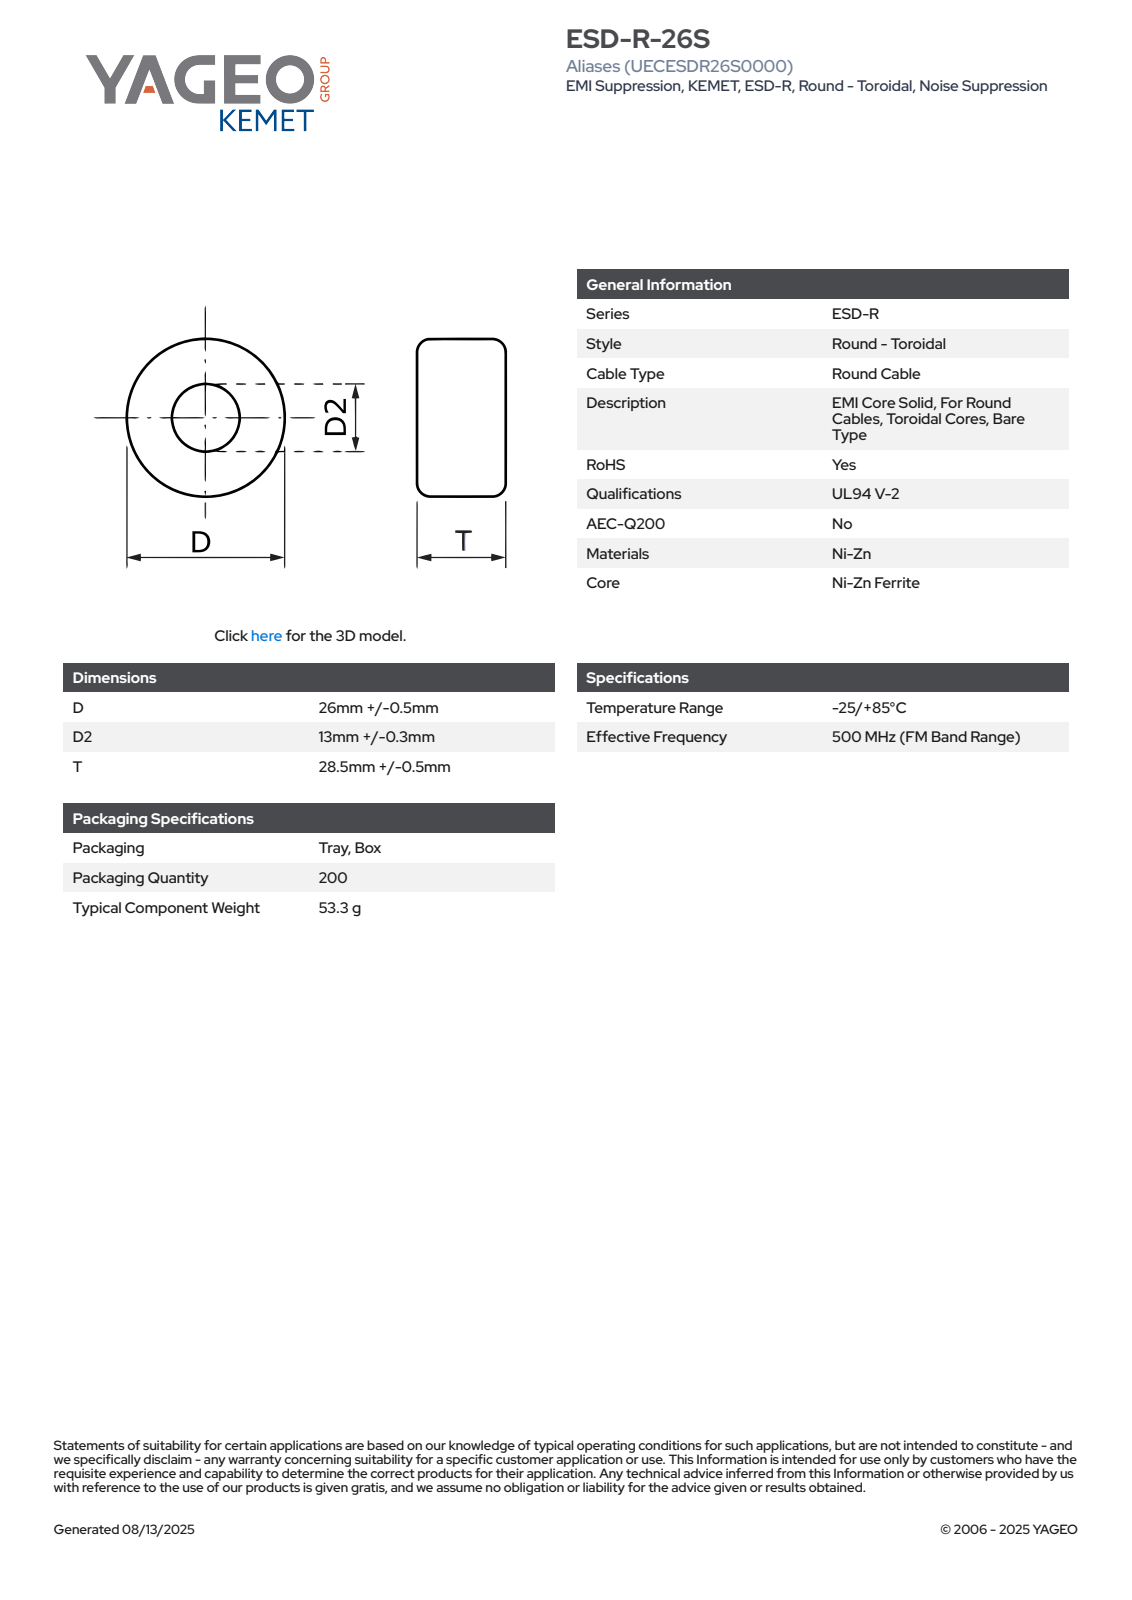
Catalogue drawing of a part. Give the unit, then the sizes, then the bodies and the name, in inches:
Units: inches
Overall size (bounding box): 1.142 × 1.044 × 1.043
Round holes (diameter × count): ⌀0.512 ×1
Round bosses / shafts (diameter × count): ⌀1.043 ×1
Partial cylindrical surfaces — rounded edges, fillets, slot ends (radius × count): R0.522 ×1
Main face-to-face distances: 1.142, 0.537, 0.604, 0.067, 0.013, 0.55, 0.592, 0.054, 0.042, 0.579
Volume: 0.74 in³ · Surface area: 6.794 in²
Bodies: 1 solid, 66 faces (24 planar, 7 cylindrical, 35 other)
Part name (STEP PRODUCT): EC_KBC_D26.5D213T29
STEP written by: SolidWorks 2021 (AUTOMOTIVE_DESIGN)
